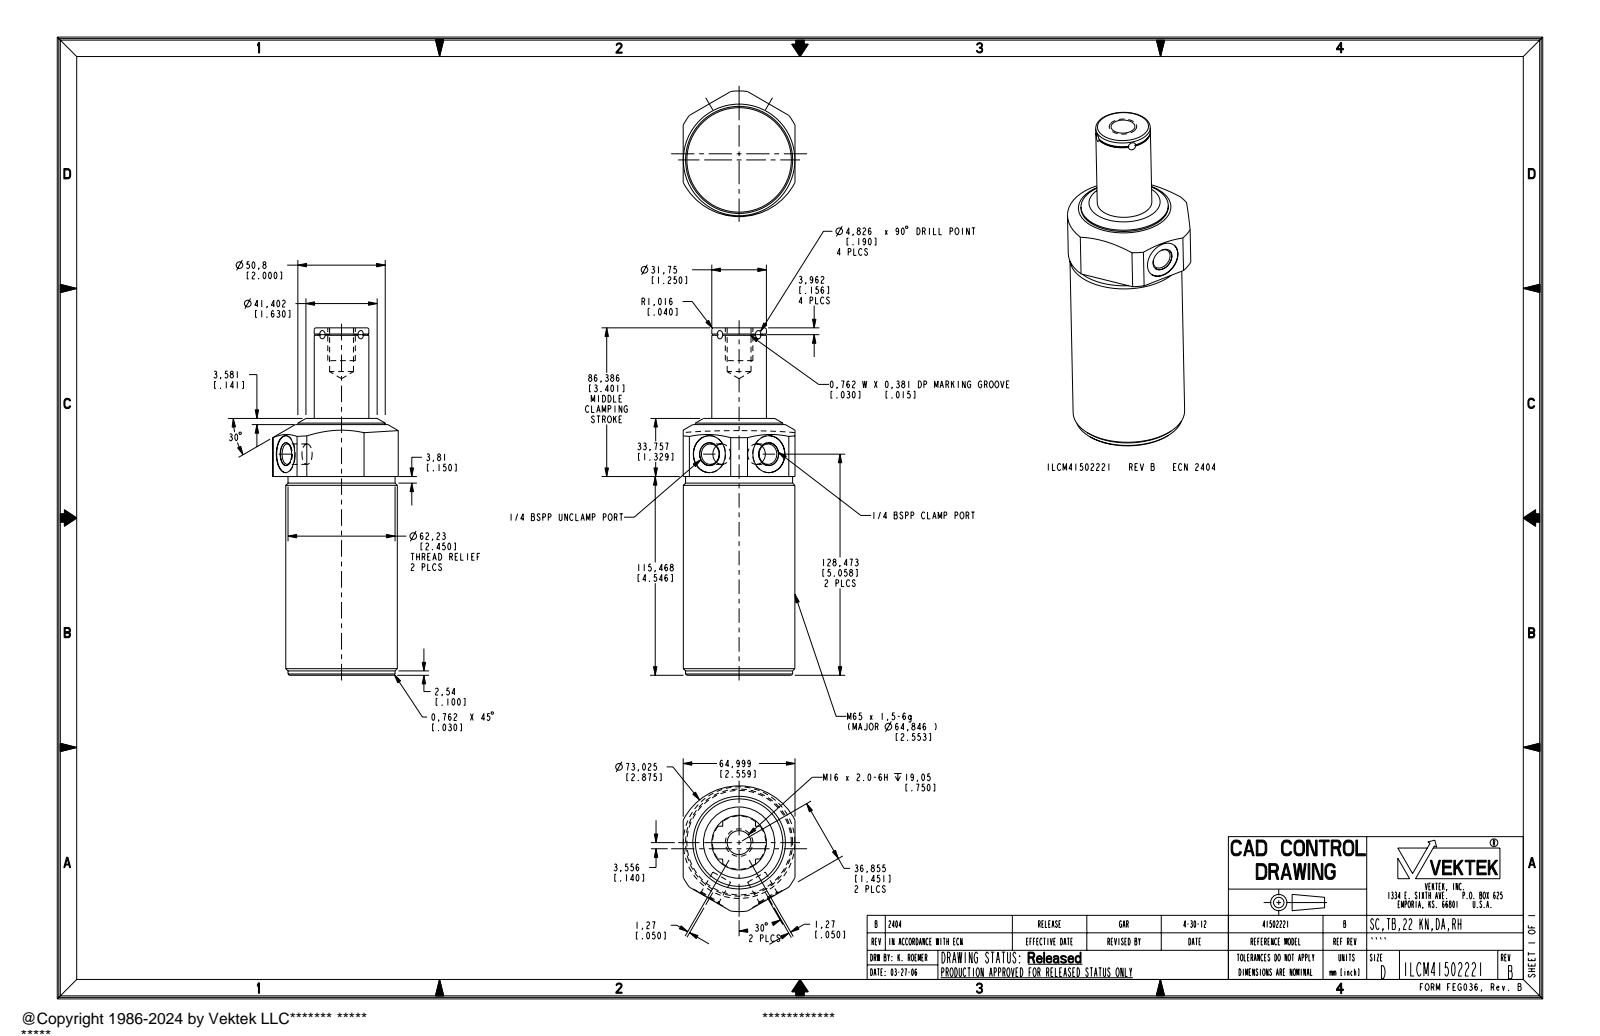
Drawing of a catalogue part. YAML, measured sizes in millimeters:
part_name: "ILCM41502221"
step_written_by: "PRO/ENGINEER BY PARAMETRIC TECHNOLOGY CORPORATION, 2007460 (AUTOMOTIVE_DESIGN_CC2)"
units: millimeters
bodies: {solids: 1, faces: 84, planar: 22, cylindrical: 36, other: 26}
overall_size: [201.85, 73.03, 65]
volume: 533163
surface_area: 46097
round_holes:
  - {diameter: 11.89, count: 2}
  - {diameter: 13.31, count: 2}
  - {diameter: 21.49, count: 2}
  - {diameter: 13.87, count: 1}
round_bosses_or_shafts:
  - {diameter: 64.85, count: 1}
  - {diameter: 62.23, count: 1}
  - {diameter: 50.8, count: 1}
  - {diameter: 31.75, count: 1}
  - {diameter: 30.99, count: 1}
  - {diameter: 16, count: 1}
partial_cylinders:
  - {radius: 36.51, count: 1}
face_to_face_distances: [65, 115.47, 149.23, 33.76, 201.86, 86.39, 52.63, 145.65, 30.18, 3.58]
